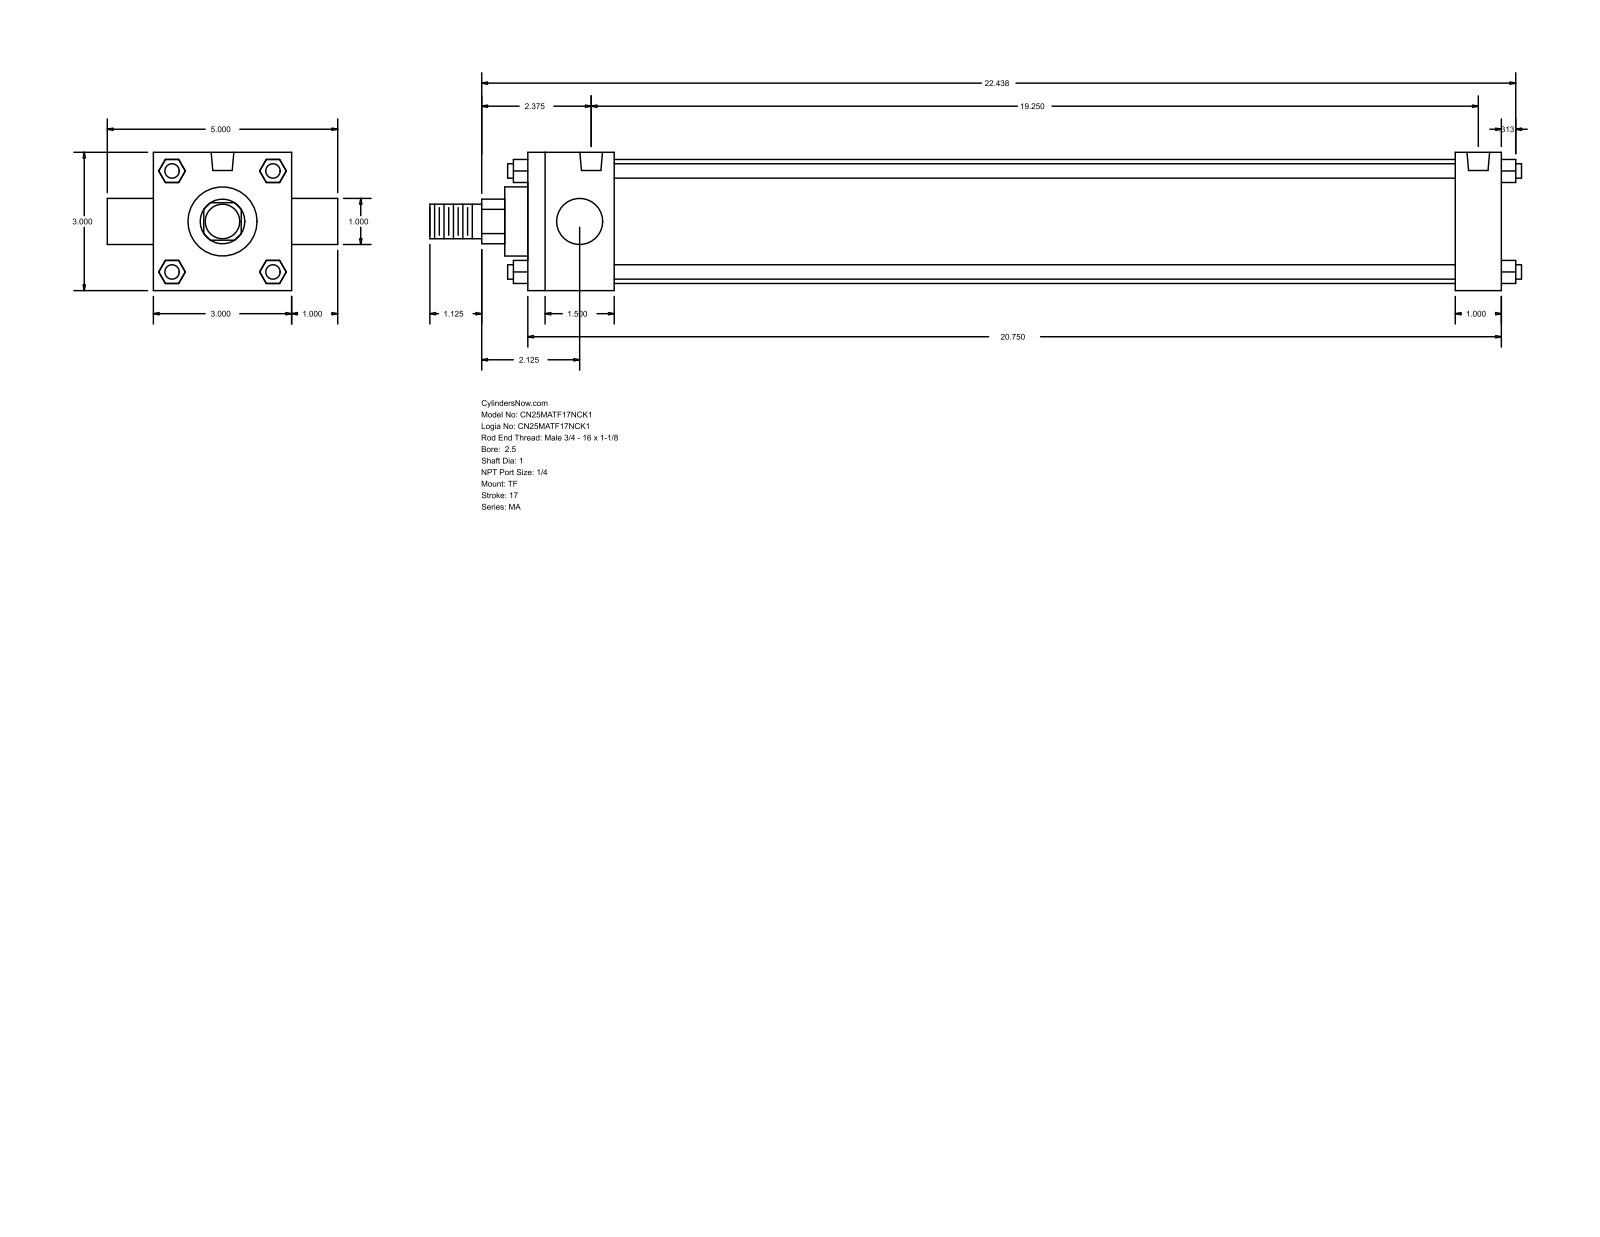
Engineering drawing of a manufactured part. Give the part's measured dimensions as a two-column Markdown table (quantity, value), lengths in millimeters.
| quantity | value |
| --- | --- |
| part name | MA_TF__0250_1 |
| STEP written by | GSSL Pune (CONFIG_CONTROL_DESIGN) |
| units | millimeters |
| bodies | 0 solids, 120 faces (92 planar, 28 cylindrical, 0 other) |
| overall size | 601.66 × 127 × 76.2 |
| round holes (diameter × count) | 7.94 × 3, 12.49 × 2 |
| round bosses / shafts (diameter × count) | 7.94 × 4, 25.4 × 2, 68.33 × 1, 38.1 × 1, 19.05 × 1 |
| partial cylindrical surfaces (radius × count) | 12.29 × 1 |
| main face-to-face distances | 76.2, 536.58, 25.4, 12.7, 47.63, 511.18, 463.55, 488.95, 101.6, 27.81 |
| hole center spacings | 488.94 |
